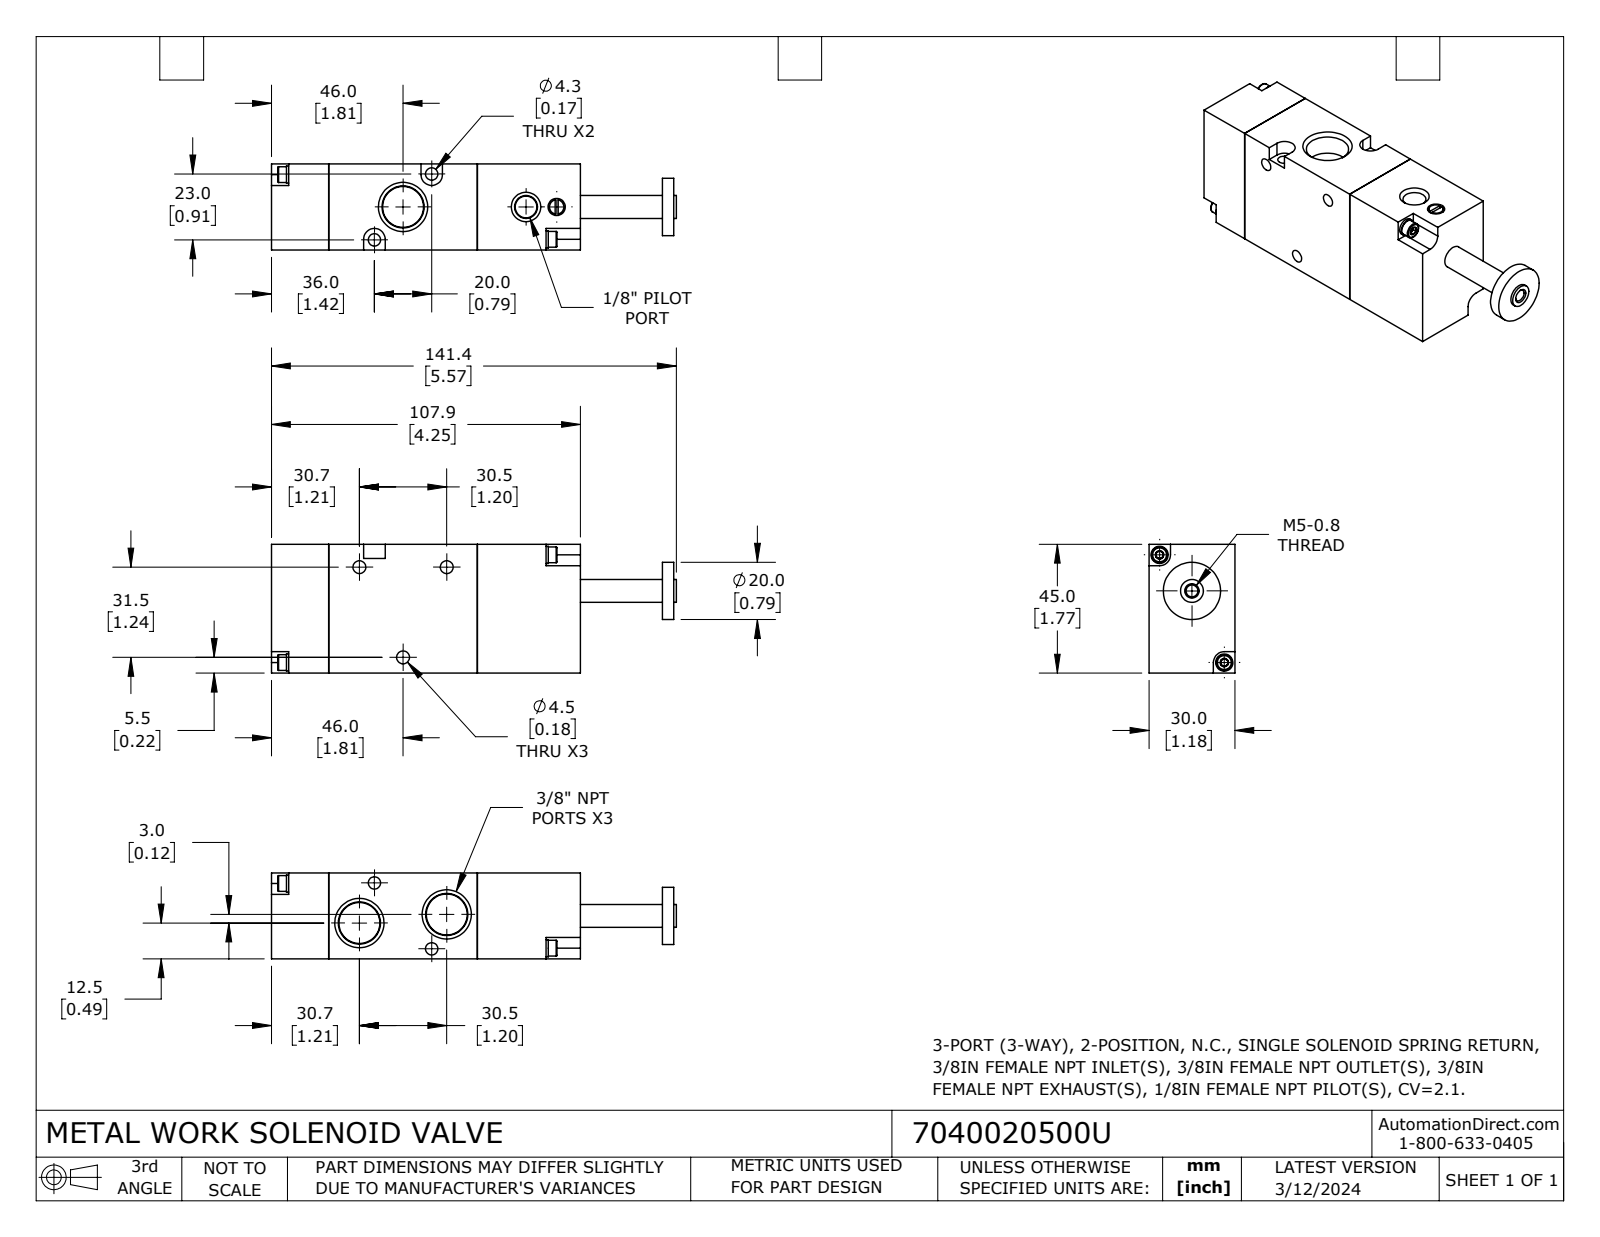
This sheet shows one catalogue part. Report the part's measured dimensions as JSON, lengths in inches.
{"part_name": "7040020500U", "step_written_by": "SolidWorks 2023 (CONFIG_CONTROL_DESIGN)", "units": "inches", "bodies": {"solids": 11, "faces": 252, "planar": 117, "cylindrical": 61, "other": 74}, "overall_size": [5.567, 1.772, 1.181], "volume_in3": 8.511, "surface_area_in2": 47.21, "round_holes": [[0.118, 4], [0.177, 3], [0.169, 2], [0.163, 1], [0.236, 1]], "round_bosses_or_shafts": [[0.236, 4], [0.217, 4], [0.787, 1], [0.315, 1], [0.197, 1]], "partial_cylinders_radius": [[0.15, 4], [0.148, 2]], "face_to_face_distances": [1.181, 2.043, 1.772, 0.787, 2.831, 1.417, 4.248, 3.461, 1.457, 0.315], "hole_center_spacings": [0.666, 0.89, 1.08, 1.378, 1.48, 1.727, 1.2, 1.201]}
